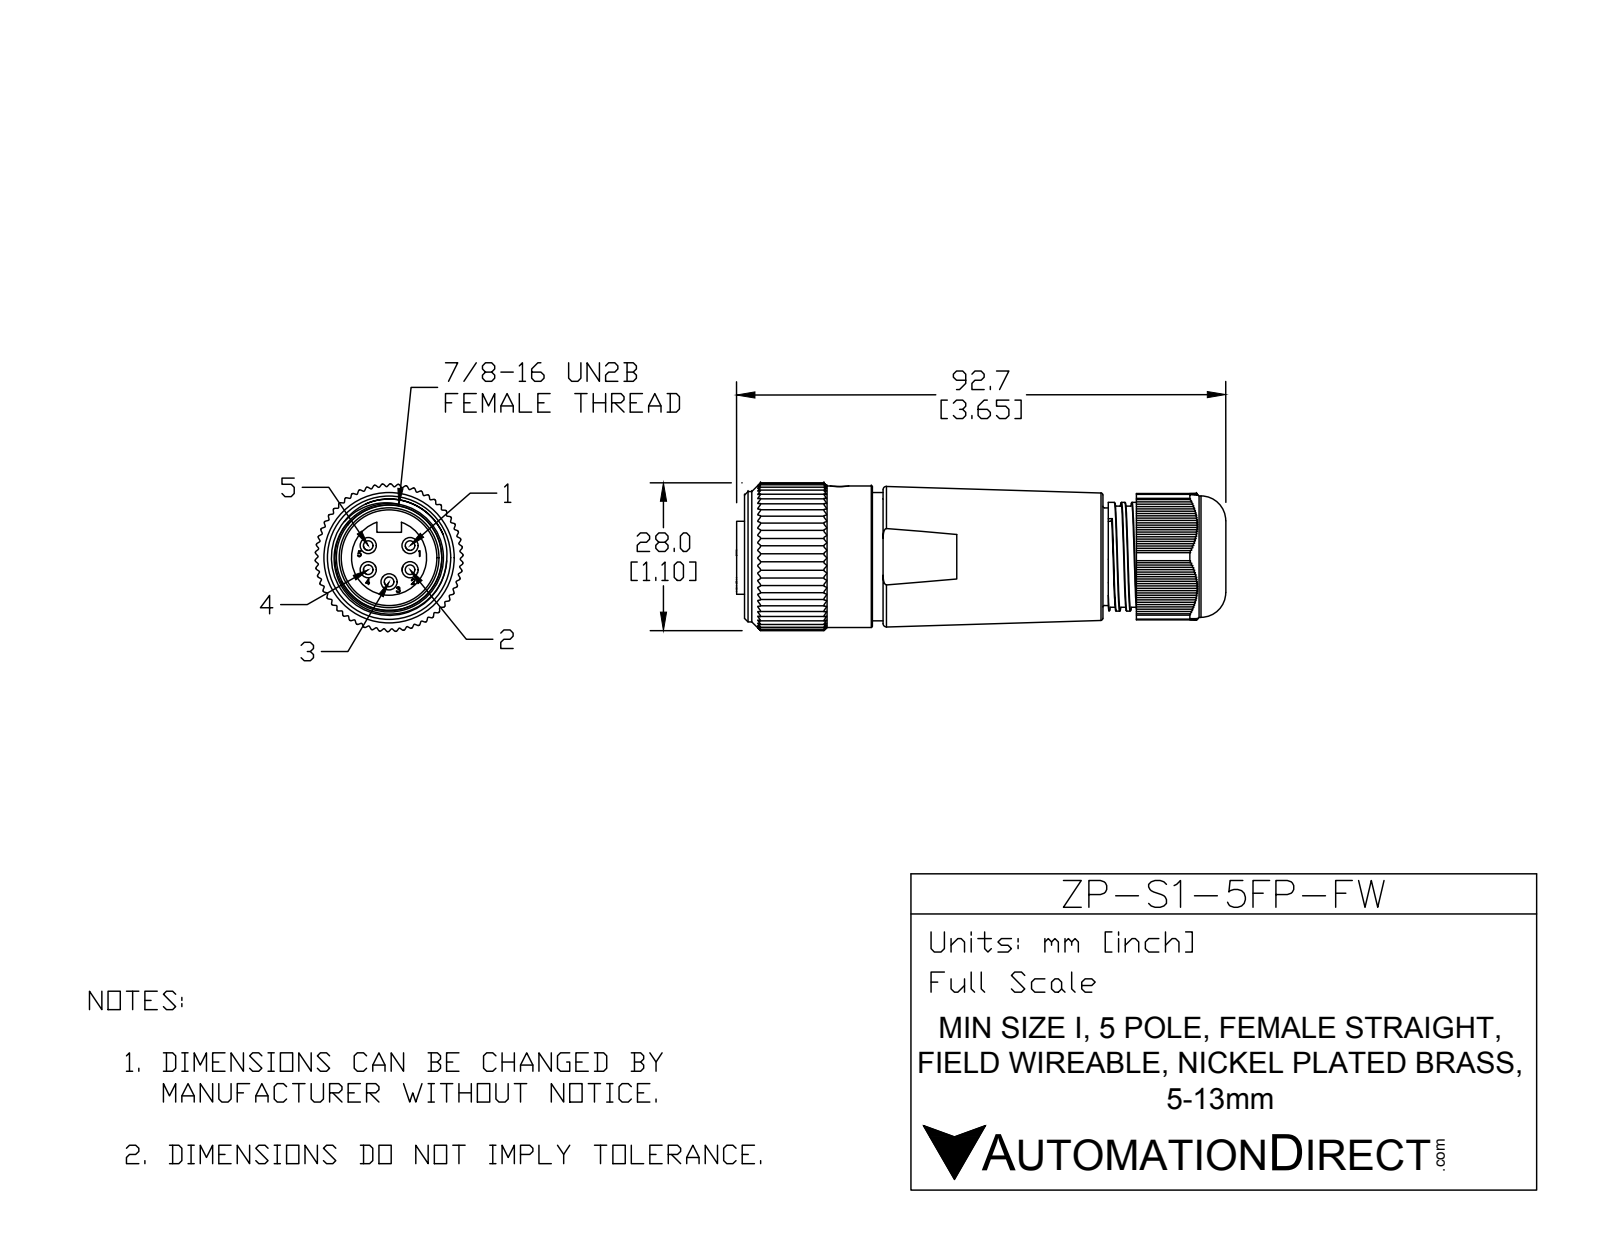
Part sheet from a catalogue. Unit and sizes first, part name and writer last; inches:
Units: inches
Overall size (bounding box): 3.652 × 1.102 × 1.102
Round holes (diameter × count): ⌀0.12 ×5, ⌀0.138 ×1, ⌀0.53 ×1, ⌀0.81 ×1, ⌀1 ×1
Round bosses / shafts (diameter × count): ⌀1.055 ×1, ⌀0.972 ×1, ⌀0.957 ×1, ⌀0.945 ×1, ⌀0.905 ×1, ⌀0.811 ×1, ⌀0.787 ×1, ⌀0.714 ×1
Partial cylindrical surfaces — rounded edges, fillets, slot ends (radius × count): R0.01 ×116, R0.008 ×58, R0.521 ×1, R0.551 ×1
Main face-to-face distances: 0.014, 0.028, 0.746, 0.043, 0.25, 2.732, 0.057, 0.652, 0.638, 0.071
Hole centre spacings: 0.18, 0.312, 0.18, 0.36
Volume: 2.657 in³ · Surface area: 18.57 in²
Bodies: 1 solid, 851 faces (469 planar, 320 cylindrical, 62 other)
Part name (STEP PRODUCT): MIN-5FP-FW
STEP written by: SolidWorks 2015 (AUTOMOTIVE_DESIGN)
